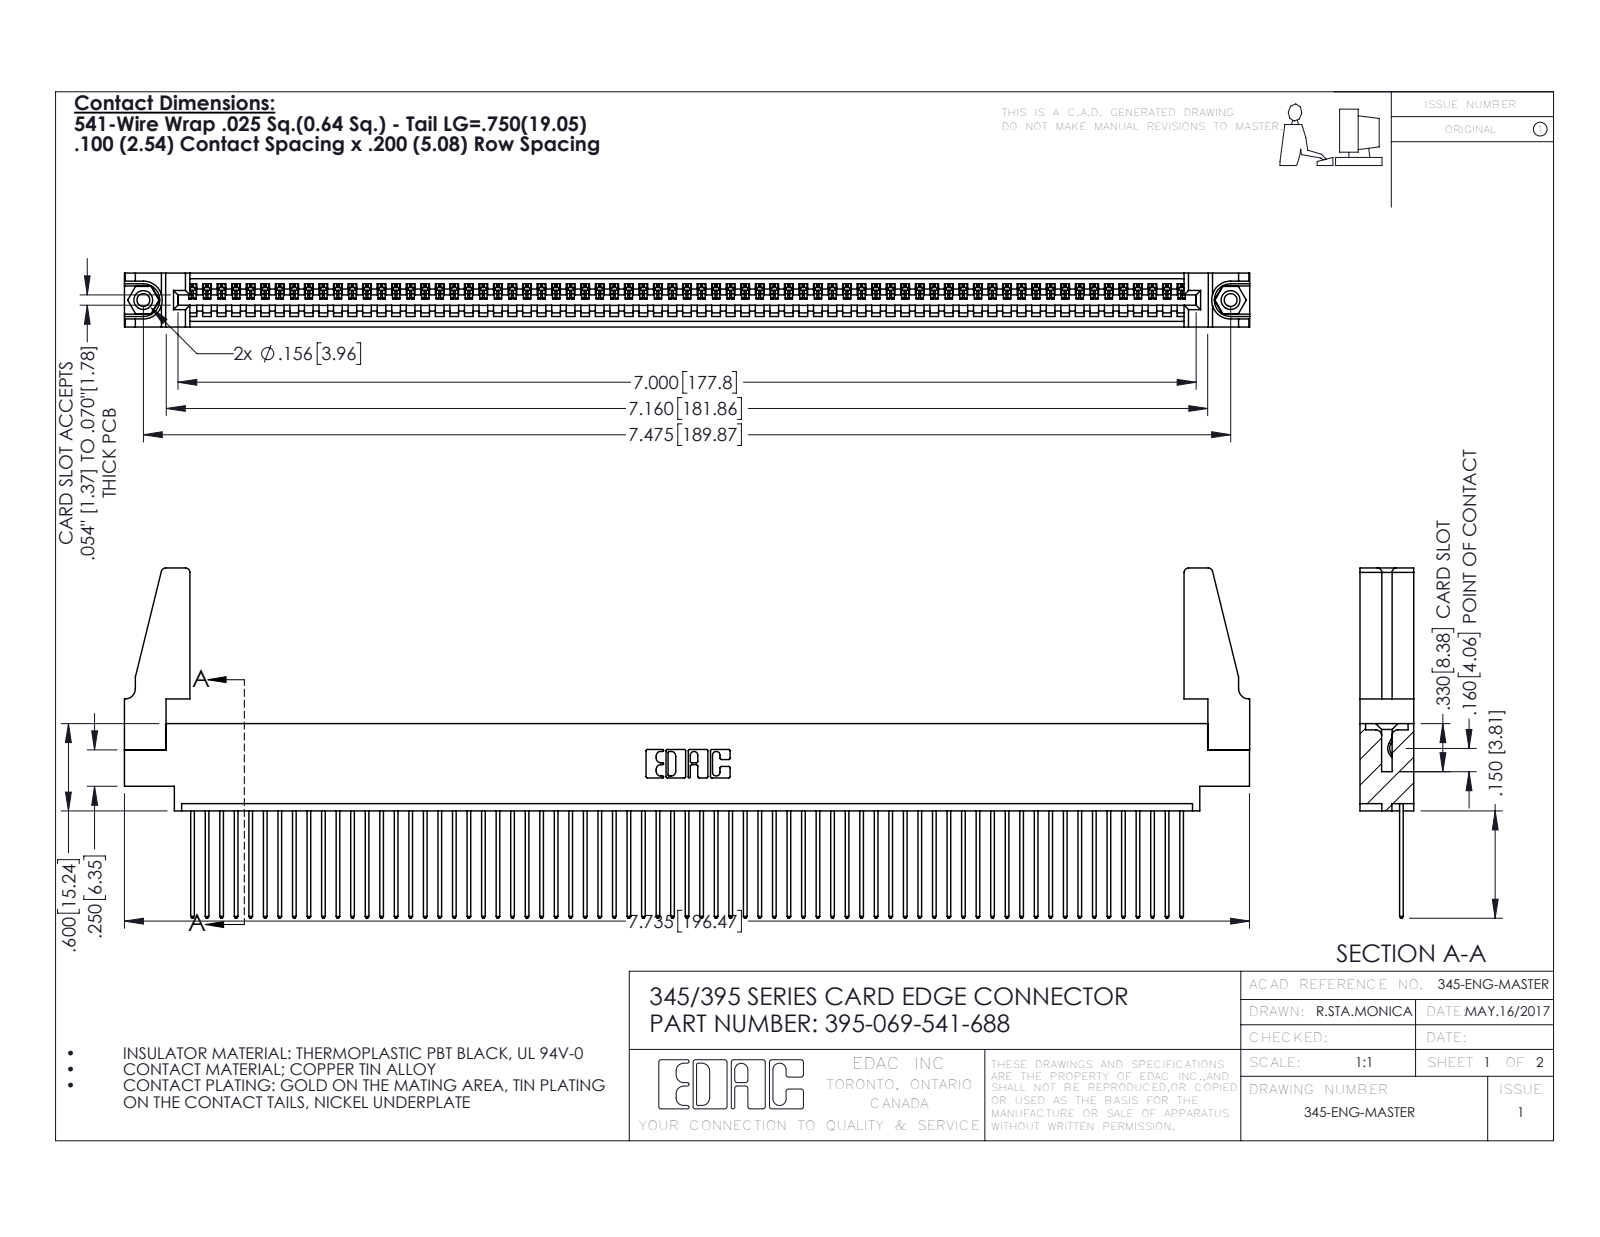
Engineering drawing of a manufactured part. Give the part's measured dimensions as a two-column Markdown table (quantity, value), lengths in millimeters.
| quantity | value |
| --- | --- |
| part name | 345-220-078_345-220-088; 395-069-541-688; 345-250-001_345-250-001-102; 345-292-001_345-293-141 (+1 more) |
| STEP written by | SolidWorks 2016 (CONFIG_CONTROL_DESIGN) |
| units | millimeters |
| bodies | 74 solids, 4256 faces (2916 planar, 1324 cylindrical, 16 other) |
| overall size | 196.5 × 61.1 × 9.4 |
| volume | 22 250 mm³ |
| surface area | 30 210 mm² |
| round holes (diameter × count) | 2.3 × 2, 3.2 × 2, 4 × 2, 1.6 × 1 |
| round bosses / shafts (diameter × count) | 3.9 × 2 |
| partial cylindrical surfaces (radius × count) | 0.2 × 138, 0.3 × 138, 0.3 × 22, 0.8 × 8, 0.2 × 6, 0.8 × 6, 0.7 × 3, 0.8 × 2 |
| main face-to-face distances | 1.8, 7.6, 9.4, 2.5, 6.9, 0.6, 5.1, 5.7, 4.4, 3.8 |
| hole center spacings | 6.9, 183.9, 189.9 |
